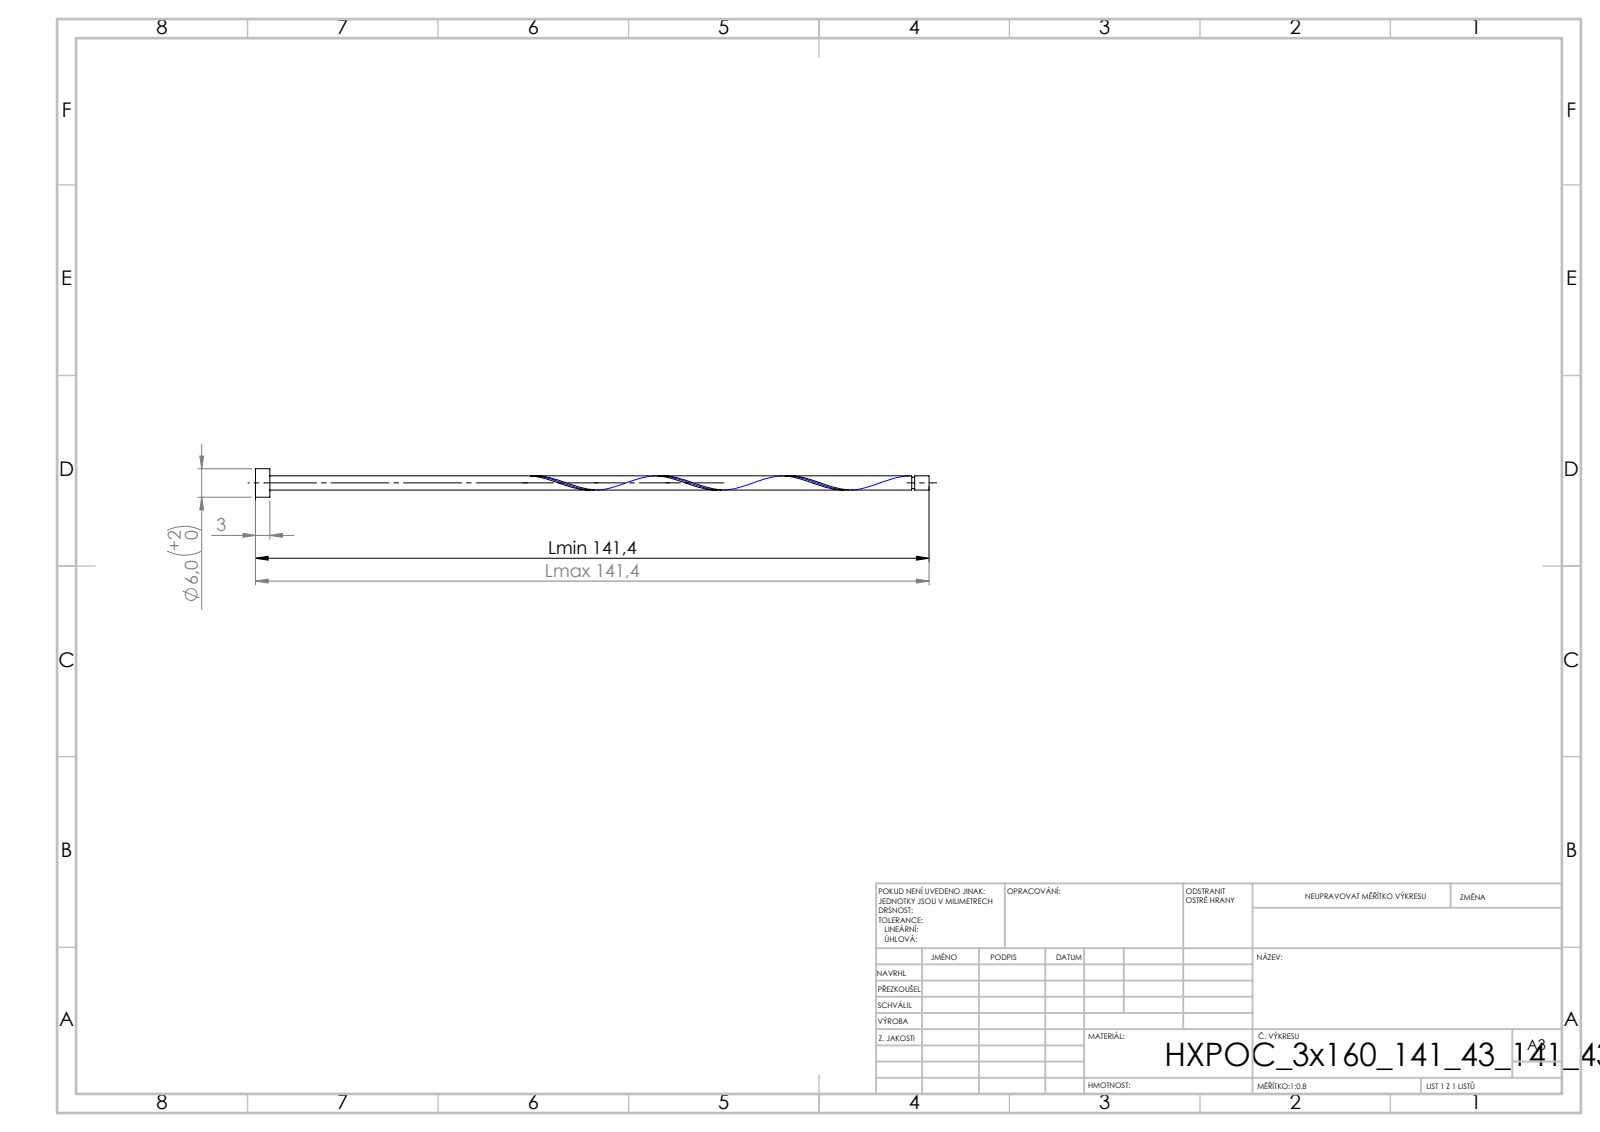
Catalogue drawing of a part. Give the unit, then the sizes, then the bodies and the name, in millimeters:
Units: millimetres
Overall size (bounding box): 141.43 × 6 × 6
Round bosses / shafts (diameter × count): ⌀6 ×1, ⌀3 ×1, ⌀2.4 ×1
Main face-to-face distances: 3, 141.43, 138.43, 138.41, 135.41, 3.02, 137.81, 134.81, 0.6, 3.62
Volume: 1 302 mm³ · Surface area: 1 949 mm²
Bodies: 1 solid, 16 faces (6 planar, 9 cylindrical, 1 other)
STEP written by: SolidWorks 2019 (CONFIG_CONTROL_DESIGN)
